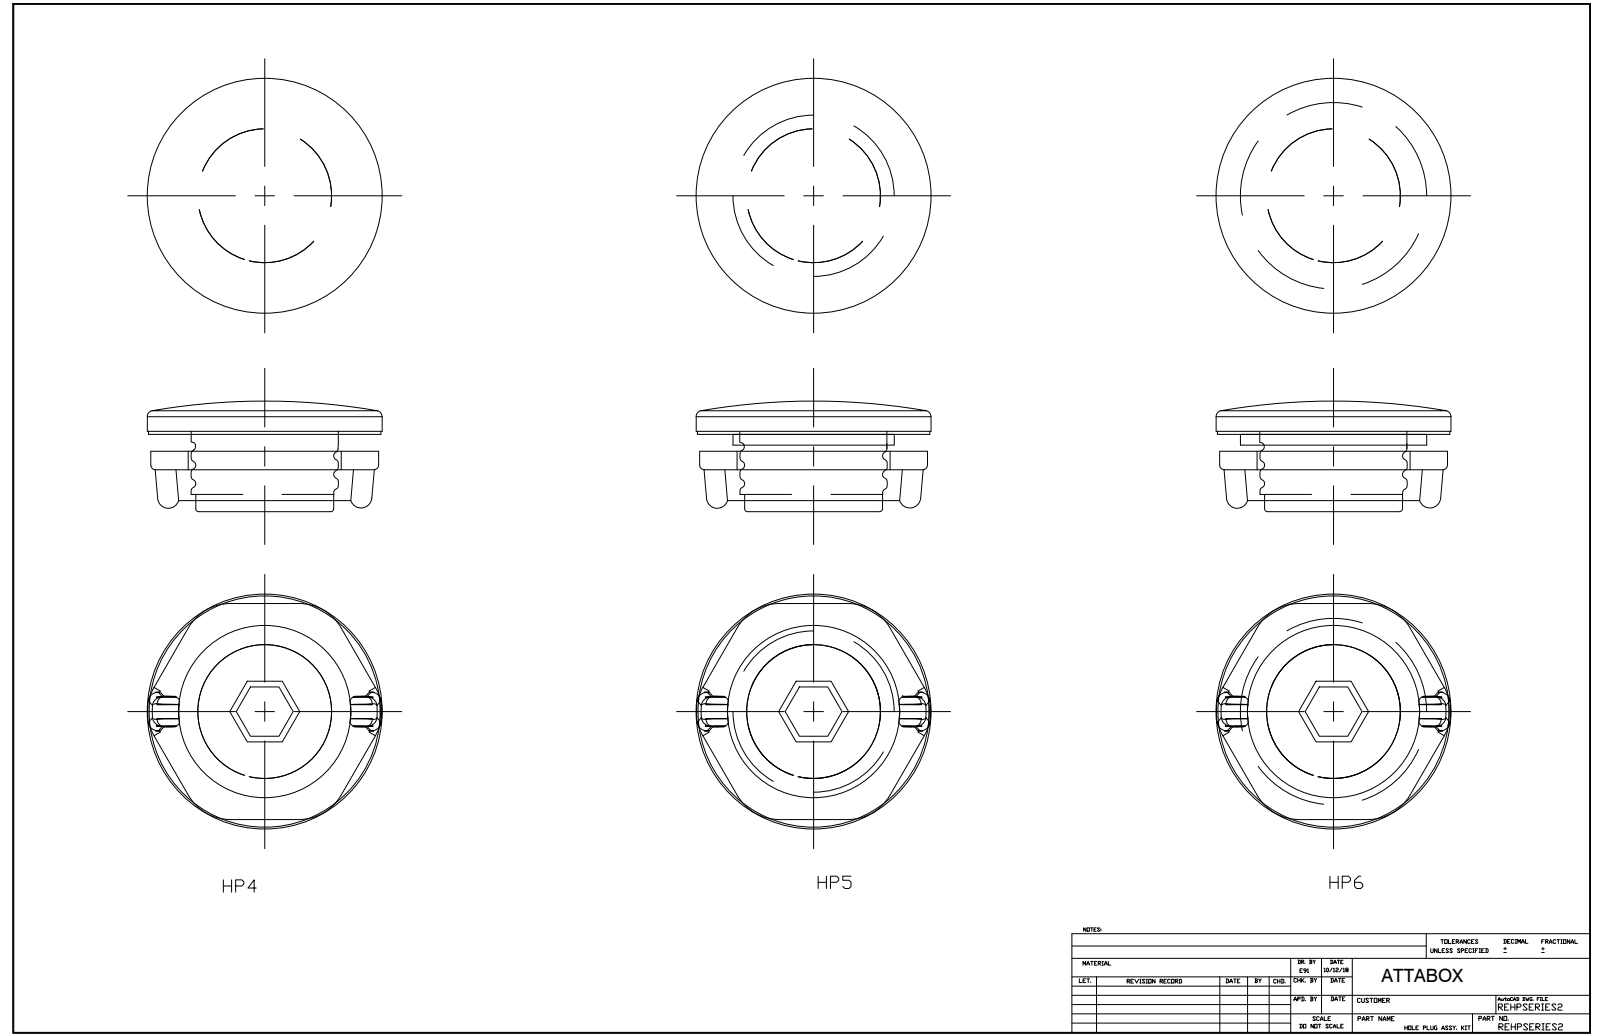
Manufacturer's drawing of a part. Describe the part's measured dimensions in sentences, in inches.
The part is named "HPSERIES2". Its 3-D file was written by "SolidWorks 2018 (AUTOMOTIVE_DESIGN)". It is 3 solids with 151 faces: 32 planar, 49 cylindrical and 70 other. Overall it measures 1.531 by 1.5 by 0.784 inches. Its volume is 0.8 cubic inches and its surface area 13.31 square inches. Round holes: 1 of diameter 0.85, 1 of diameter 0.89. Round bosses or shafts: 1 of diameter 1.5, 1 of diameter 1.48, 1 of diameter 0.79. Partial cylindrical surfaces (rounded edges, fillets, slot ends): 14 of radius 0.03, 8 of radius 0.01, 8 of radius 0.08, 6 of radius 0.196, 4 of radius 0.009, 2 of radius 0.095, 1 of radius 0.02. The main face-to-face distances are 0.125, 0.214, 0.089, 0.224, 0.099, 0.12, 0.245, 0.334, 0.344, 0.4.
